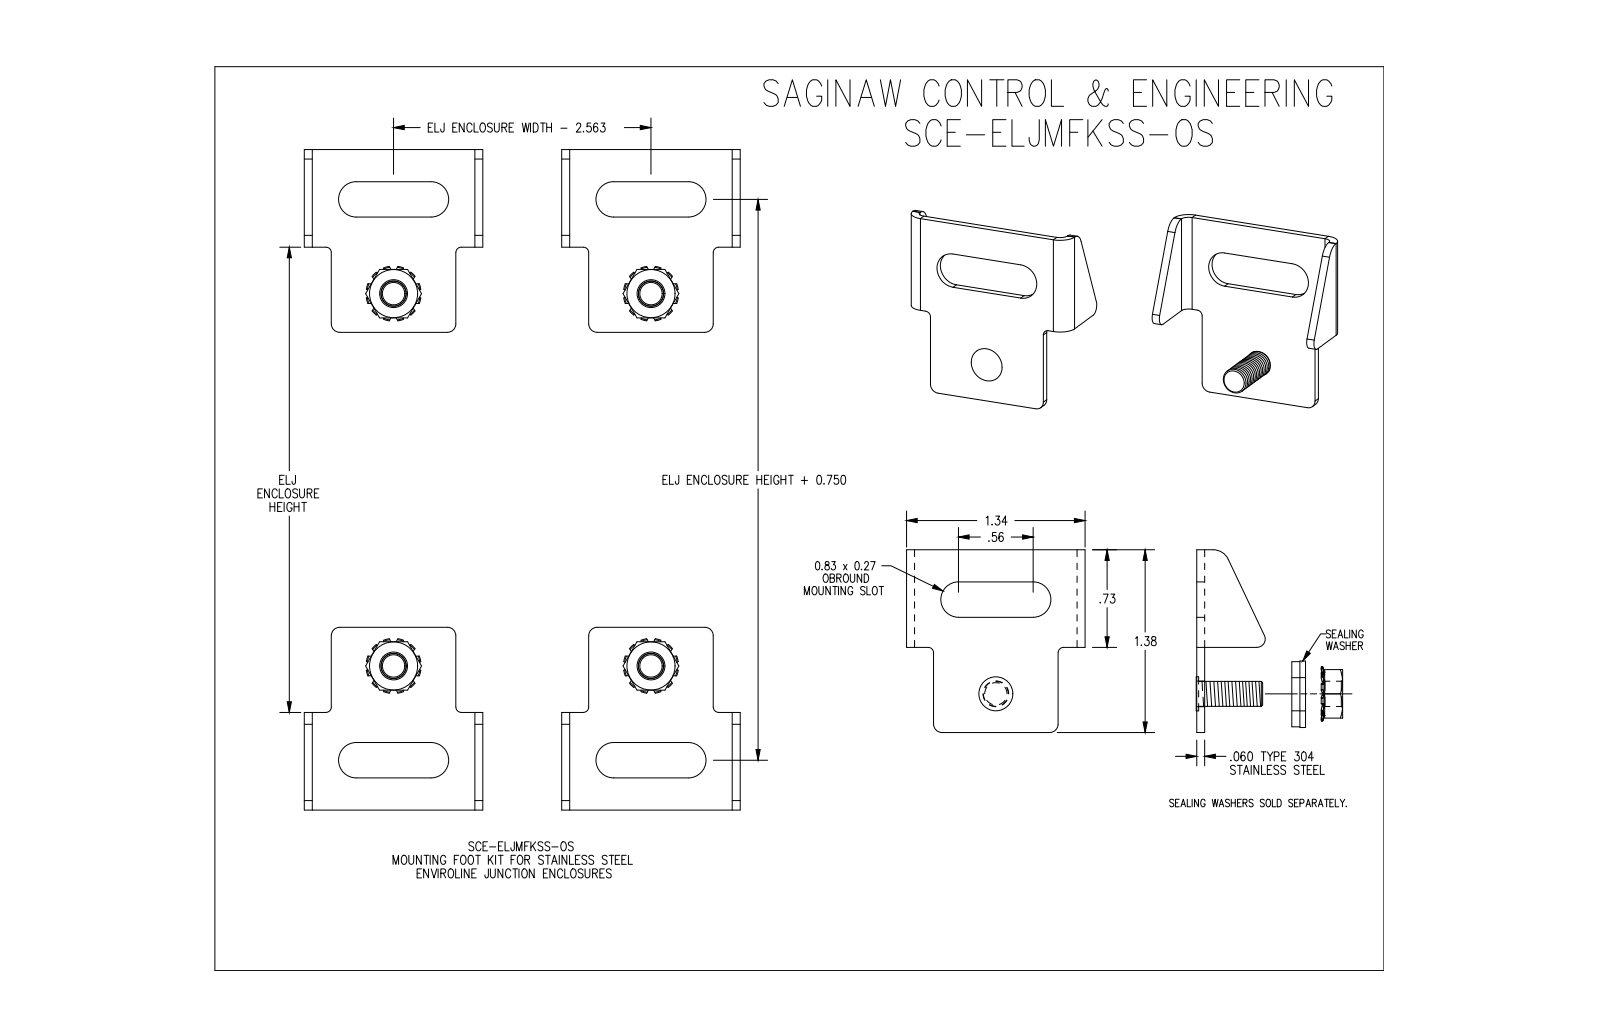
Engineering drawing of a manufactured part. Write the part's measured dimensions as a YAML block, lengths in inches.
part_name: "SCE-ELJMFKSS-OS"
step_written_by: "SolidWorks 2019 (CONFIG_CONTROL_DESIGN)"
units: inches
bodies: {solids: 12, faces: 444, planar: 300, cylindrical: 72, other: 72}
overall_size: [4.969, 3.281, 0.52]
volume: 0.529
surface_area: 19.93
round_holes:
  - {diameter: 0.19, count: 4}
  - {diameter: 0.193, count: 4}
round_bosses_or_shafts:
  - {diameter: 0.256, count: 4}
  - {diameter: 0.188, count: 4}
partial_cylinders:
  - {radius: 0.063, count: 9}
  - {radius: 0.04, count: 8}
  - {radius: 0.133, count: 8}
  - {radius: 0.06, count: 4}
  - {radius: 0.12, count: 4}
  - {radius: 0.125, count: 2}
  - {radius: 0.062, count: 1}
face_to_face_distances: [0.06, 1.937, 1.284, 1.344, 3.221, 1.878, 1.938, 3.281, 0.594, 0.654]
hole_center_spacings: [1.938, 2.801, 3.406]
